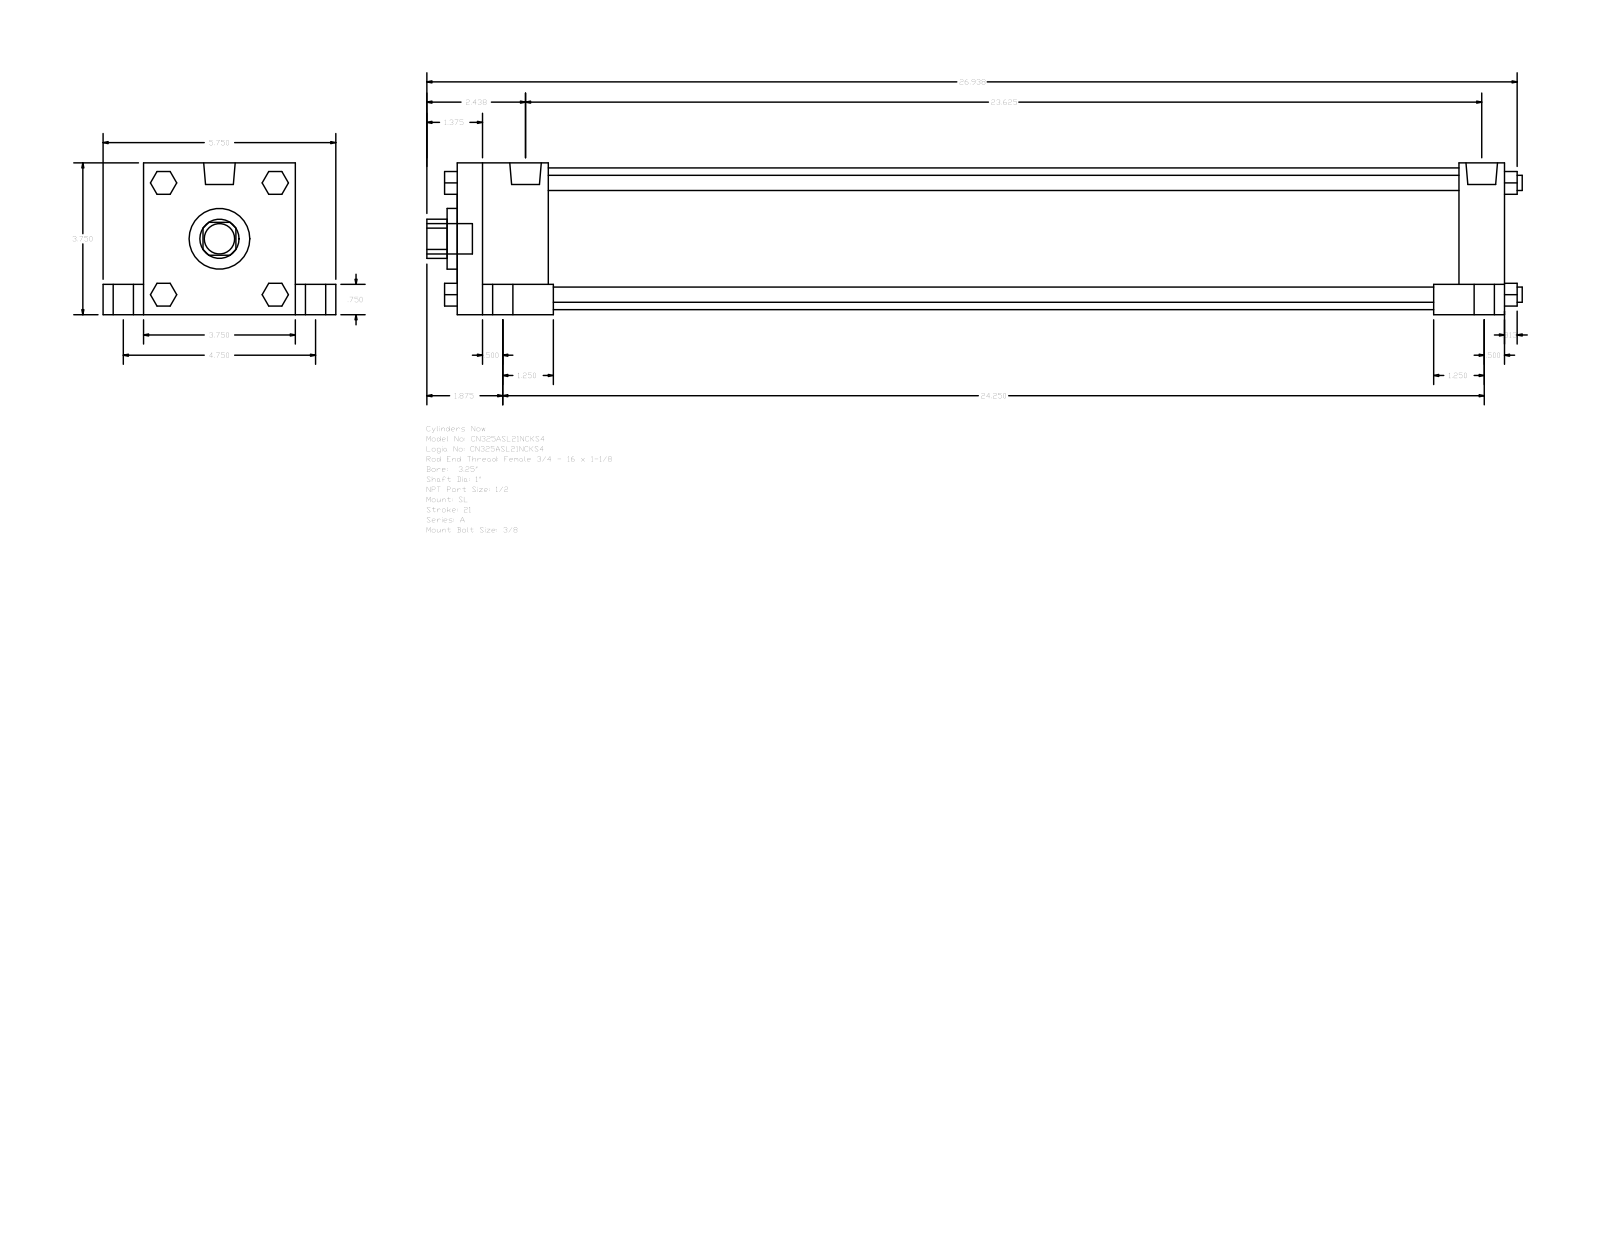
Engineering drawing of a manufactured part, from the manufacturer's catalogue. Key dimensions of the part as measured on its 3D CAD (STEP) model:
Part name (STEP PRODUCT): A_SL__0325_1
STEP written by: GSSL Pune (CONFIG_CONTROL_DESIGN)
Units: millimetres
Bodies: 0 solids, 150 faces (114 planar, 36 cylindrical, 0 other)
Overall size (bounding box): 687.39 × 146.05 × 95.25
Round holes (diameter × count): ⌀25.4 ×1, ⌀38.1 ×1, ⌀88.9 ×1
Round bosses / shafts (diameter × count): ⌀19.05 ×5, ⌀12.7 ×4, ⌀9.53 ×4, ⌀8.73 ×4, ⌀19.77 ×2
Partial cylindrical surfaces — rounded edges, fillets, slot ends (radius × count): R12.29 ×1
Main face-to-face distances: 95.24, 657.22, 19.05, 25.41, 120.65, 76.19, 15.87, 28.57, 57.15, 628.65
